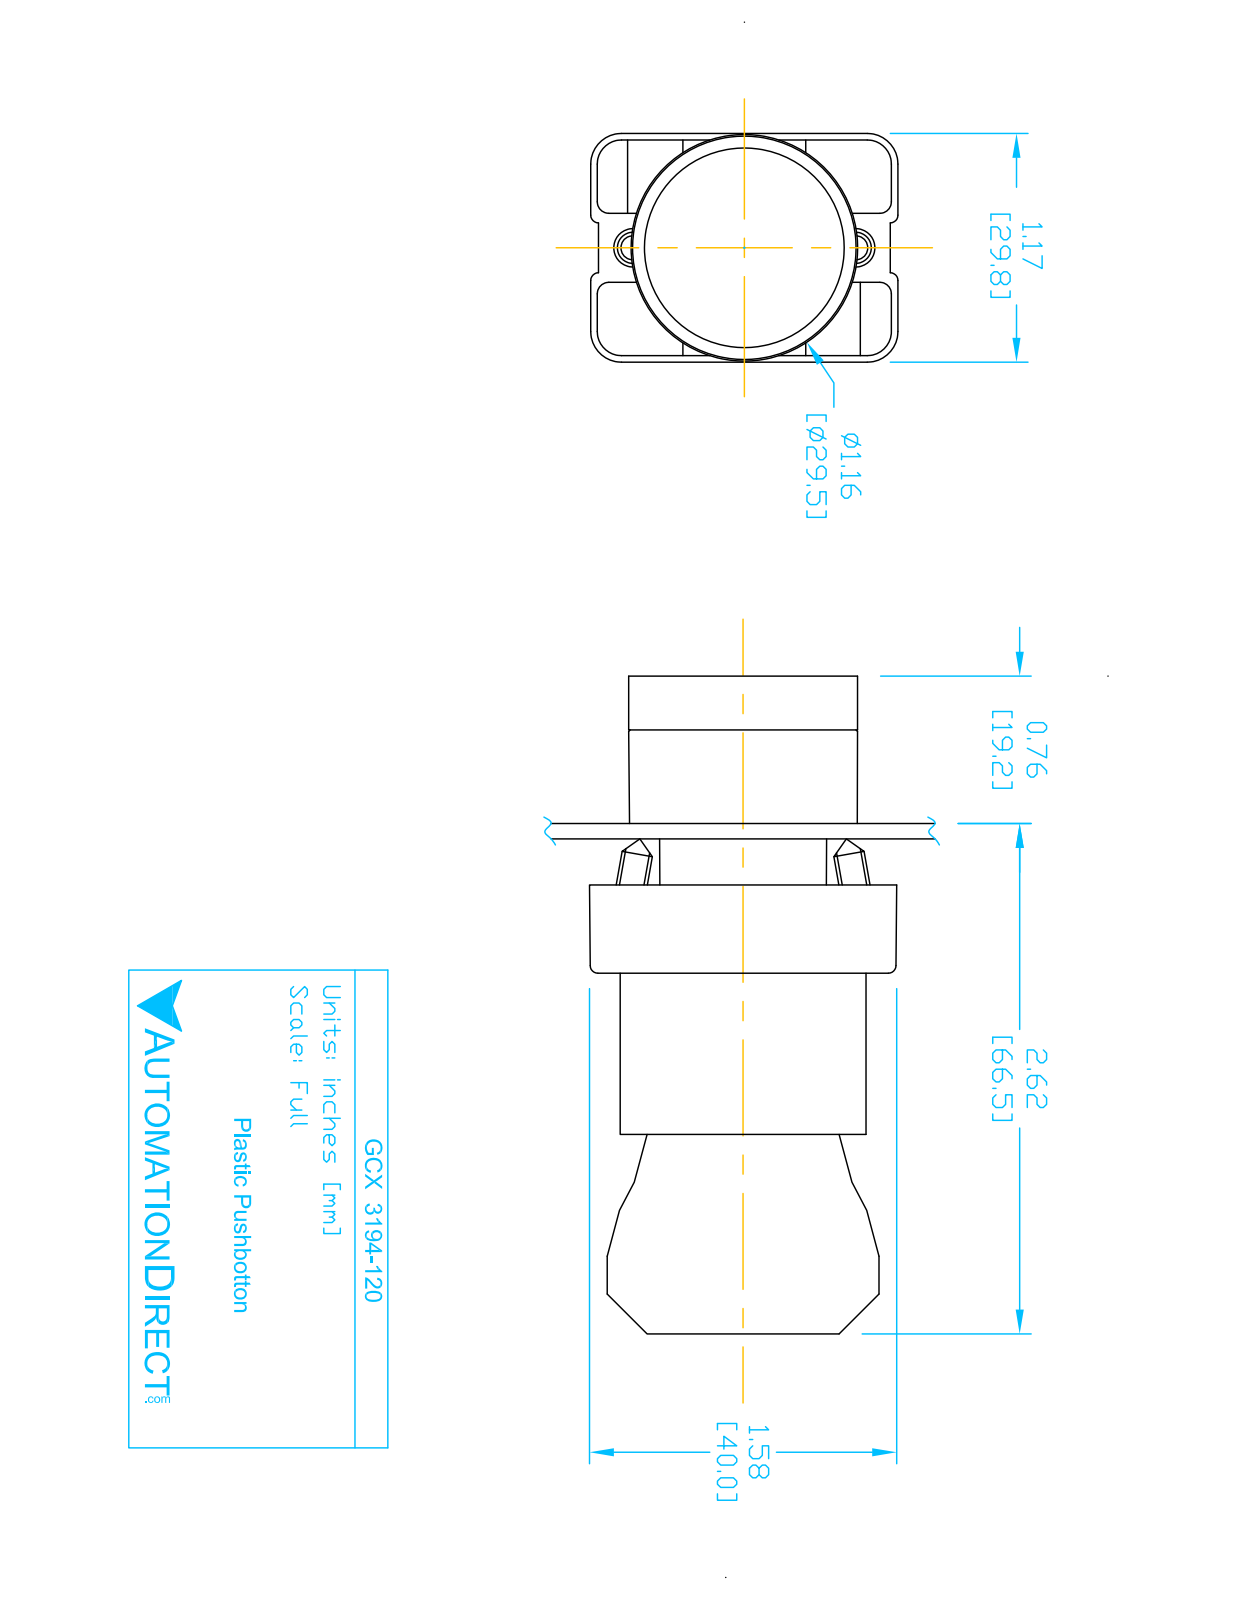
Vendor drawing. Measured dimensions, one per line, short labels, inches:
name: CONTACT BLOCK; GCX3194-120; ECX1050; ECX3029-2 (+1 more)
written by: SolidWorks 2016 (AUTOMOTIVE_DESIGN)
unit: in
bodies: 8 solids, 431 faces (252 planar, 148 cylindrical, 31 other)
size: 3.319 × 1.581 × 1.177
volume: 2.794 in³; area: 38.77 in²
holes: 2× ⌀0.079, 2× ⌀0.124, 2× ⌀0.13, 1× ⌀0.087, 1× ⌀0.197, 1× ⌀0.469, 1× ⌀0.878, 1× ⌀0.888, 1× ⌀1.024
bosses: 4× ⌀0.157, 1× ⌀1.175, 1× ⌀1.004, 1× ⌀0.945, 1× ⌀0.856, 1× ⌀0.78, 1× ⌀0.504
rounds: 24× R0.059, 12× R0.041, 12× R0.124, 12× R0.157, 8× R0.039, 2× R0.128, 1× R0.02, 1× R0.063
face distances: 0.827, 0.579, 2.02, 1.193, 1.171, 0.276, 2.295, 1.469, 0.031, 0.033
hole spacings: 0.236, 0.544, 0.472, 0.49
